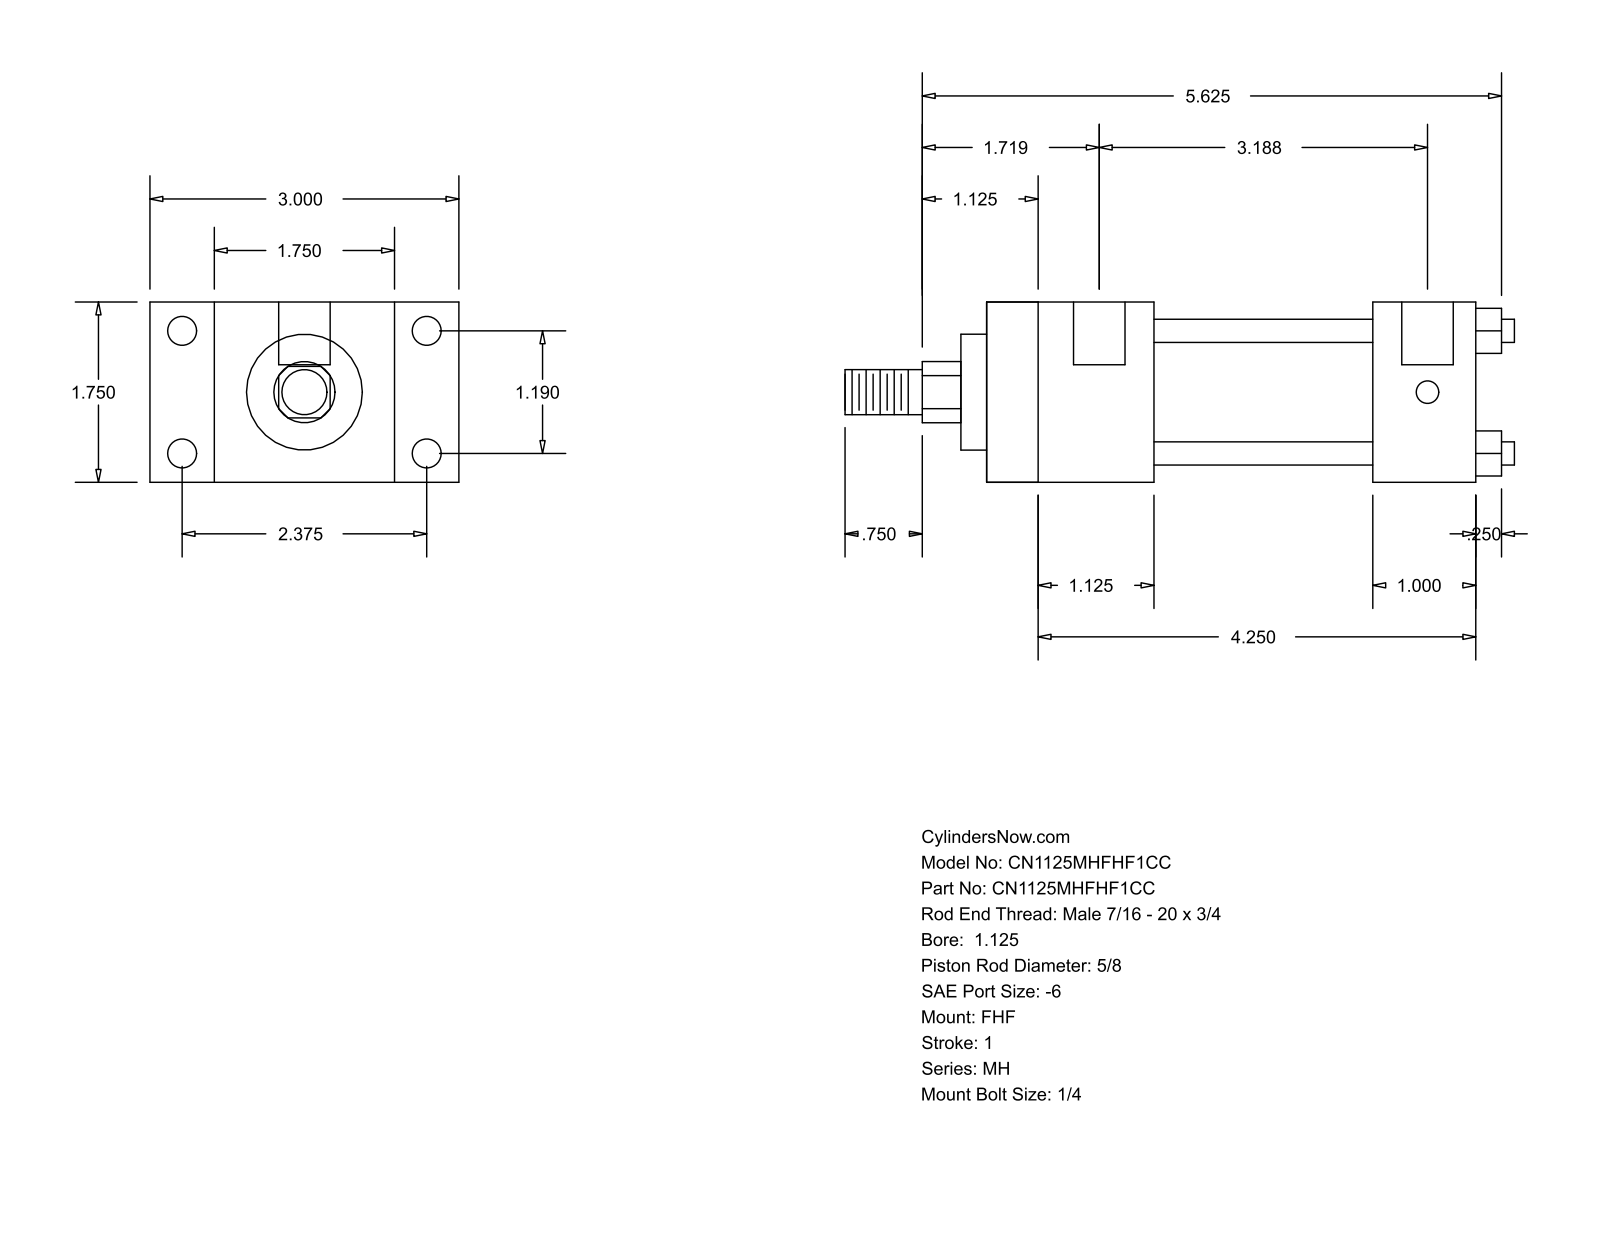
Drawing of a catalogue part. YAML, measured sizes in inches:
part_name: "MH_FHF__0112_0.625"
step_written_by: "GSSL Pune (CONFIG_CONTROL_DESIGN)"
units: inches
bodies: {solids: 0, faces: 88, planar: 60, cylindrical: 28, other: 0}
overall_size: [6.5, 3, 1.75]
round_holes:
  - {diameter: 0.219, count: 4}
  - {diameter: 0.281, count: 4}
  - {diameter: 0.5, count: 2}
round_bosses_or_shafts:
  - {diameter: 0.225, count: 4}
  - {diameter: 1.375, count: 1}
  - {diameter: 1.125, count: 1}
  - {diameter: 0.625, count: 1}
  - {diameter: 0.437, count: 1}
partial_cylinders:
  - {radius: 0.297, count: 1}
face_to_face_distances: [1.75, 0.625, 2.375, 1.625, 3, 4.75, 3.125, 3.75, 2.125, 1]
hole_center_spacings: [1.19, 2.375, 2.656, 3.063, 0.125, 3.187]
